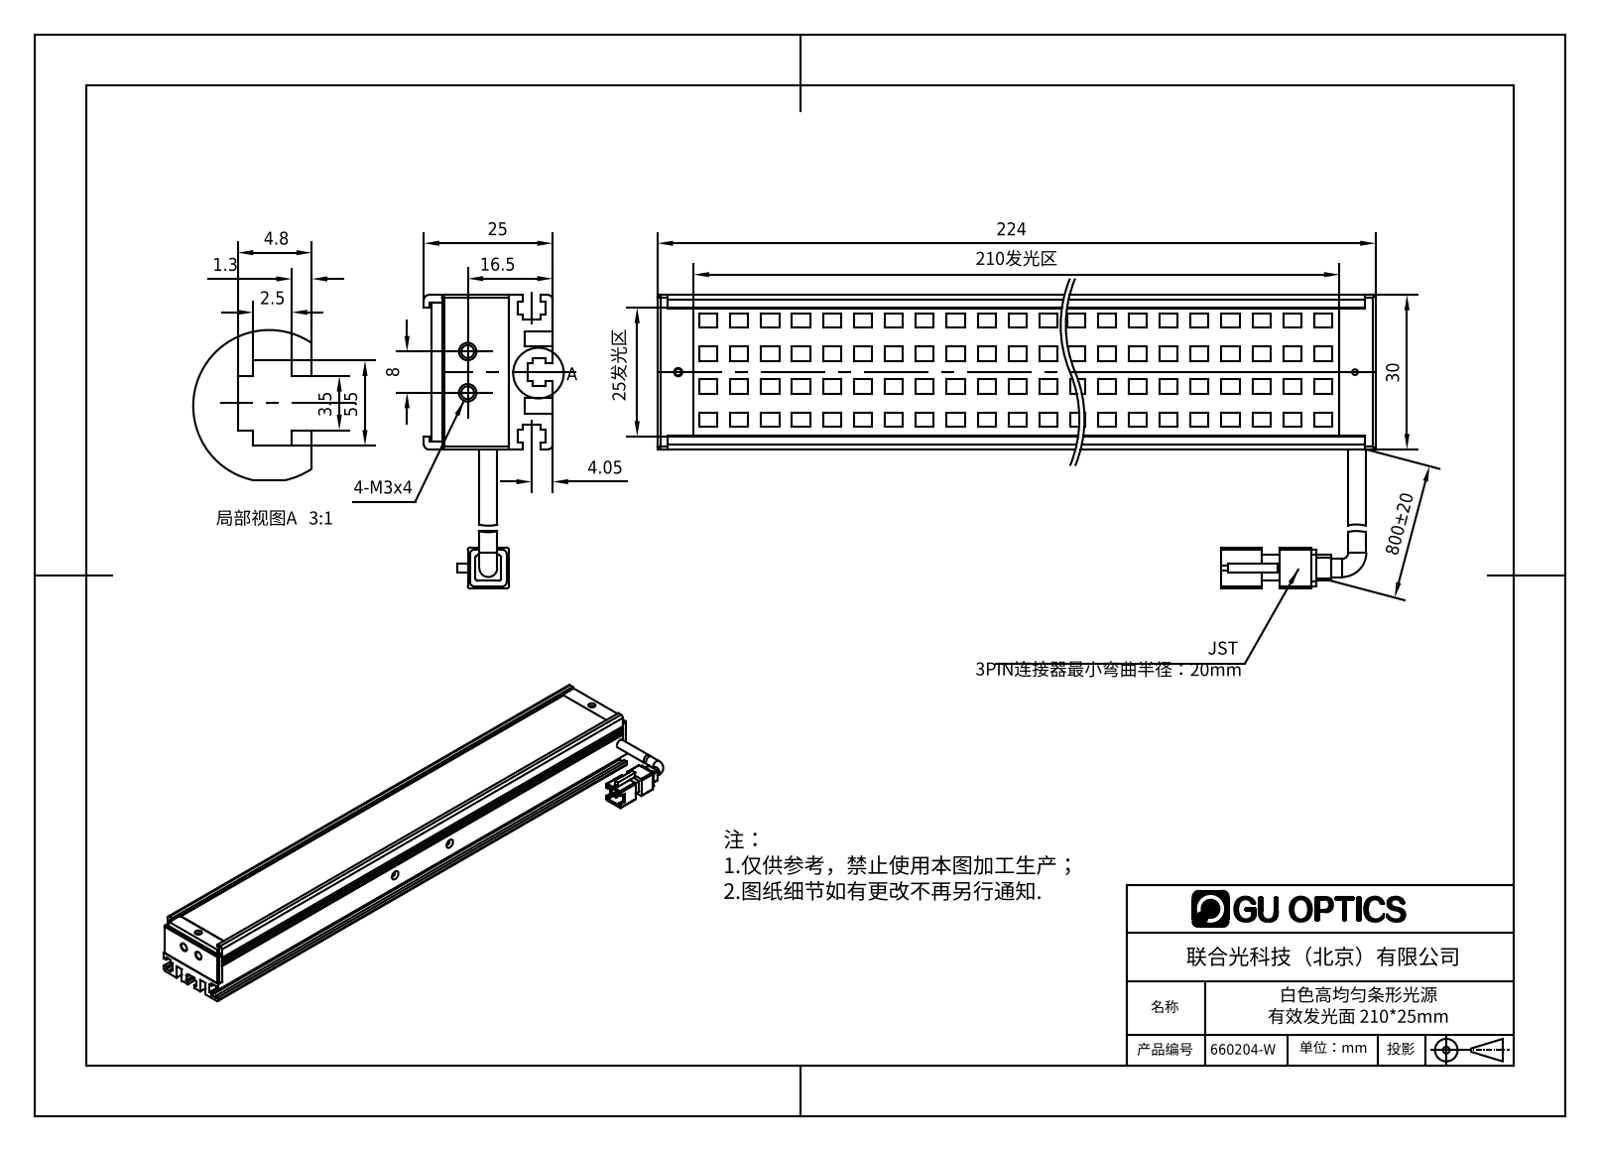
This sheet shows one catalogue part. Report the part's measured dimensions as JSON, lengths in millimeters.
{"part_name": "660204-W", "step_written_by": "SolidWorks 2016 (AUTOMOTIVE_DESIGN)", "units": "millimeters", "bodies": {"solids": 6, "faces": 1144, "planar": 958, "cylindrical": 83, "other": 103}, "overall_size": [224, 57, 25], "volume_mm3": 77133, "surface_area_mm2": 78469, "round_holes": [[1.6, 5], [1.5, 2], [1.7, 2], [2.5, 2], [2.8, 2], [3, 2], [1.1, 1], [1.25, 1], [2, 1]], "round_bosses_or_shafts": [[3.5, 2]], "partial_cylinders_radius": [[1, 12], [0.5, 8], [1.65, 1]], "face_to_face_distances": [1, 13, 2, 2.5, 3, 27.5, 9.5, 4.5, 12, 8.5], "hole_center_spacings": [216, 7, 93, 93.23, 123, 123.18, 216.11, 8]}
